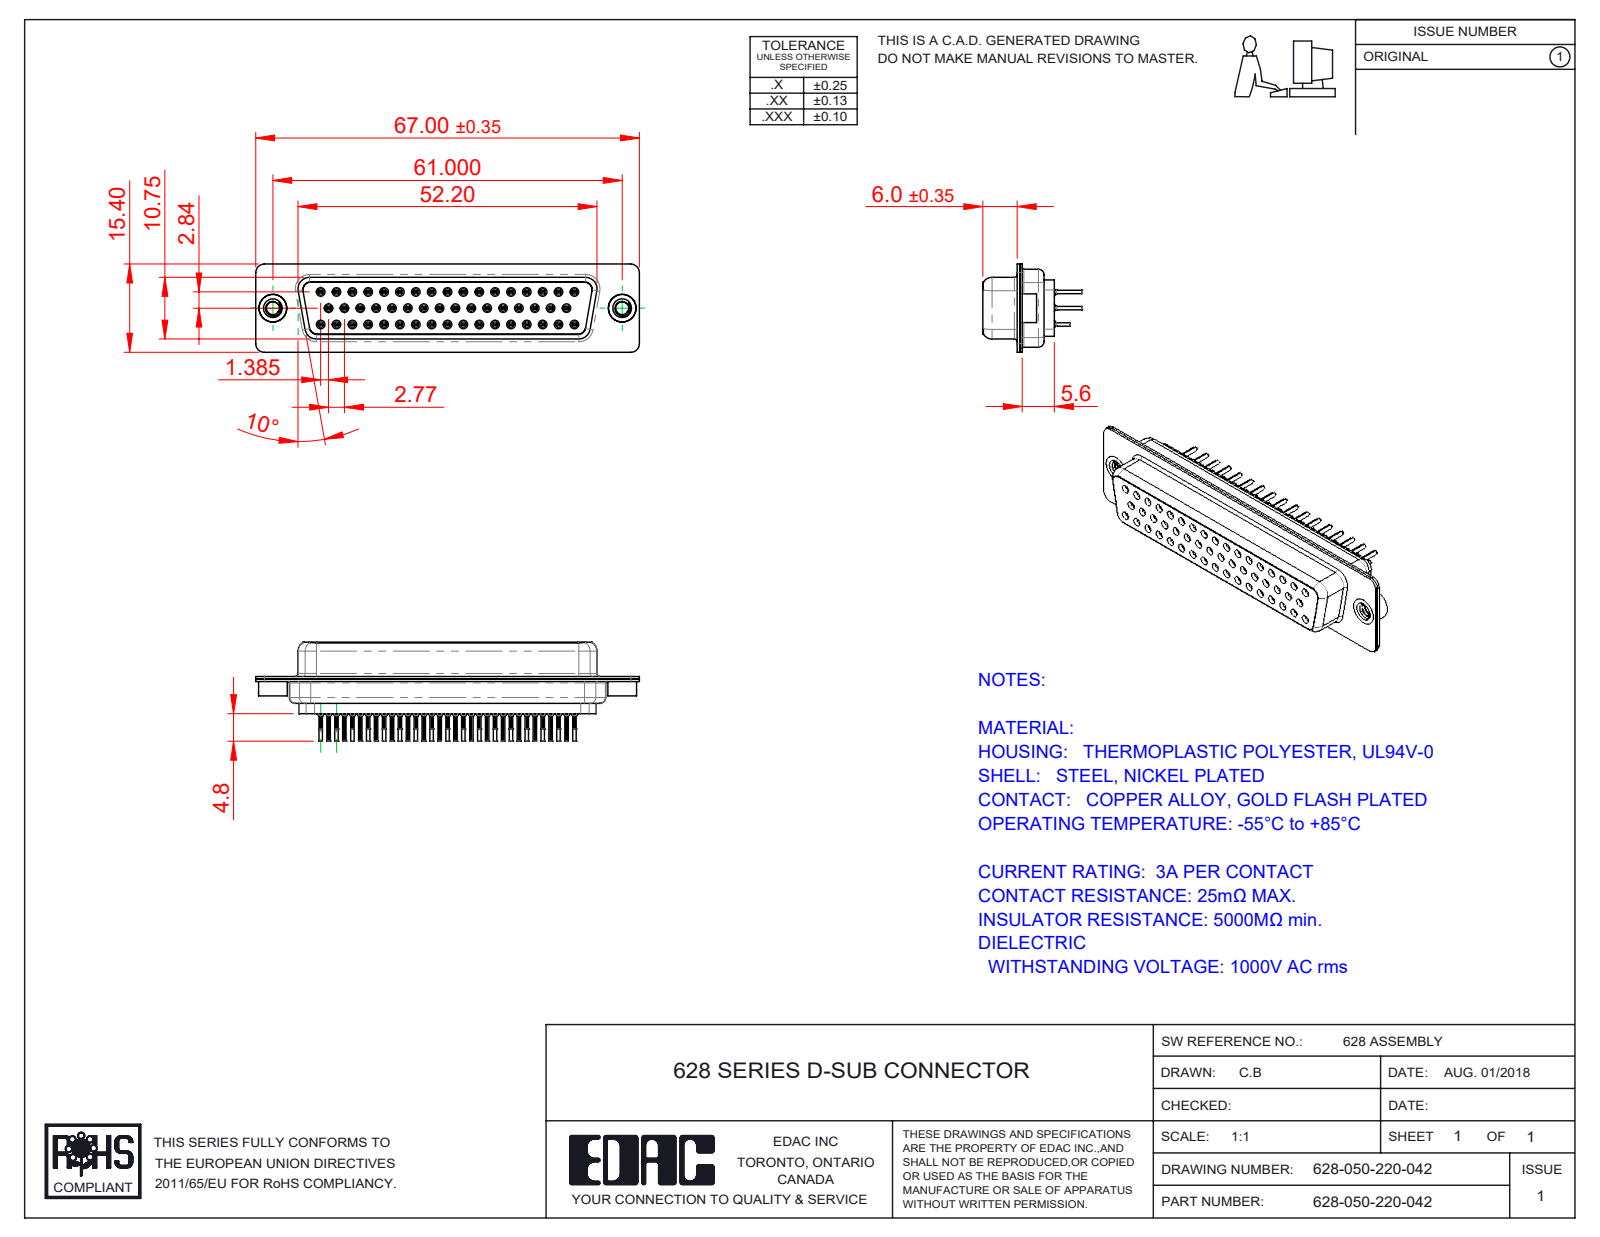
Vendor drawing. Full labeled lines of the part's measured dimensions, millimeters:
Part name (STEP PRODUCT): 628 4-40 Threaded Rivet; 628 Shell Front_50 Contacts; 628 Contact Row 2_20L; 628-050-220-042 (+4 more)
STEP written by: SolidWorks 2020 (CONFIG_CONTROL_DESIGN)
Units: millimetres
Bodies: 55 solids, 6625 faces (1617 planar, 1785 cylindrical, 3223 other)
Overall size (bounding box): 67 × 17.3 × 15.4
Volume: 6 717 mm³ · Surface area: 15 265 mm²
Round holes (diameter × count): ⌀0.2 ×50, ⌀0.8 ×50, ⌀0.9 ×50, ⌀1.1 ×50, ⌀1.6 ×50, ⌀1.7 ×17, ⌀2.26 ×2, ⌀4 ×2, ⌀4.05 ×2, ⌀4.85 ×2
Round bosses / shafts (diameter × count): ⌀2 ×50, ⌀1.5 ×50, ⌀1.2 ×50, ⌀0.6 ×50, ⌀5 ×2, ⌀4.95 ×2, ⌀4.8 ×2
Partial cylindrical surfaces — rounded edges, fillets, slot ends (radius × count): R0.1 ×100, R0.28 ×33, R1.5 ×16, R2 ×12, R1.35 ×8, R0.25 ×4, R0.5 ×4, R0.6 ×4
Main face-to-face distances: 0.45, 0.4, 11.33, 1.87, 10.3, 0.9, 6.05, 6.5, 1.8, 6.45
Hole centre spacings: 3.16, 2.77, 5.54, 8.31, 11.08, 13.85, 16.62, 19.39
